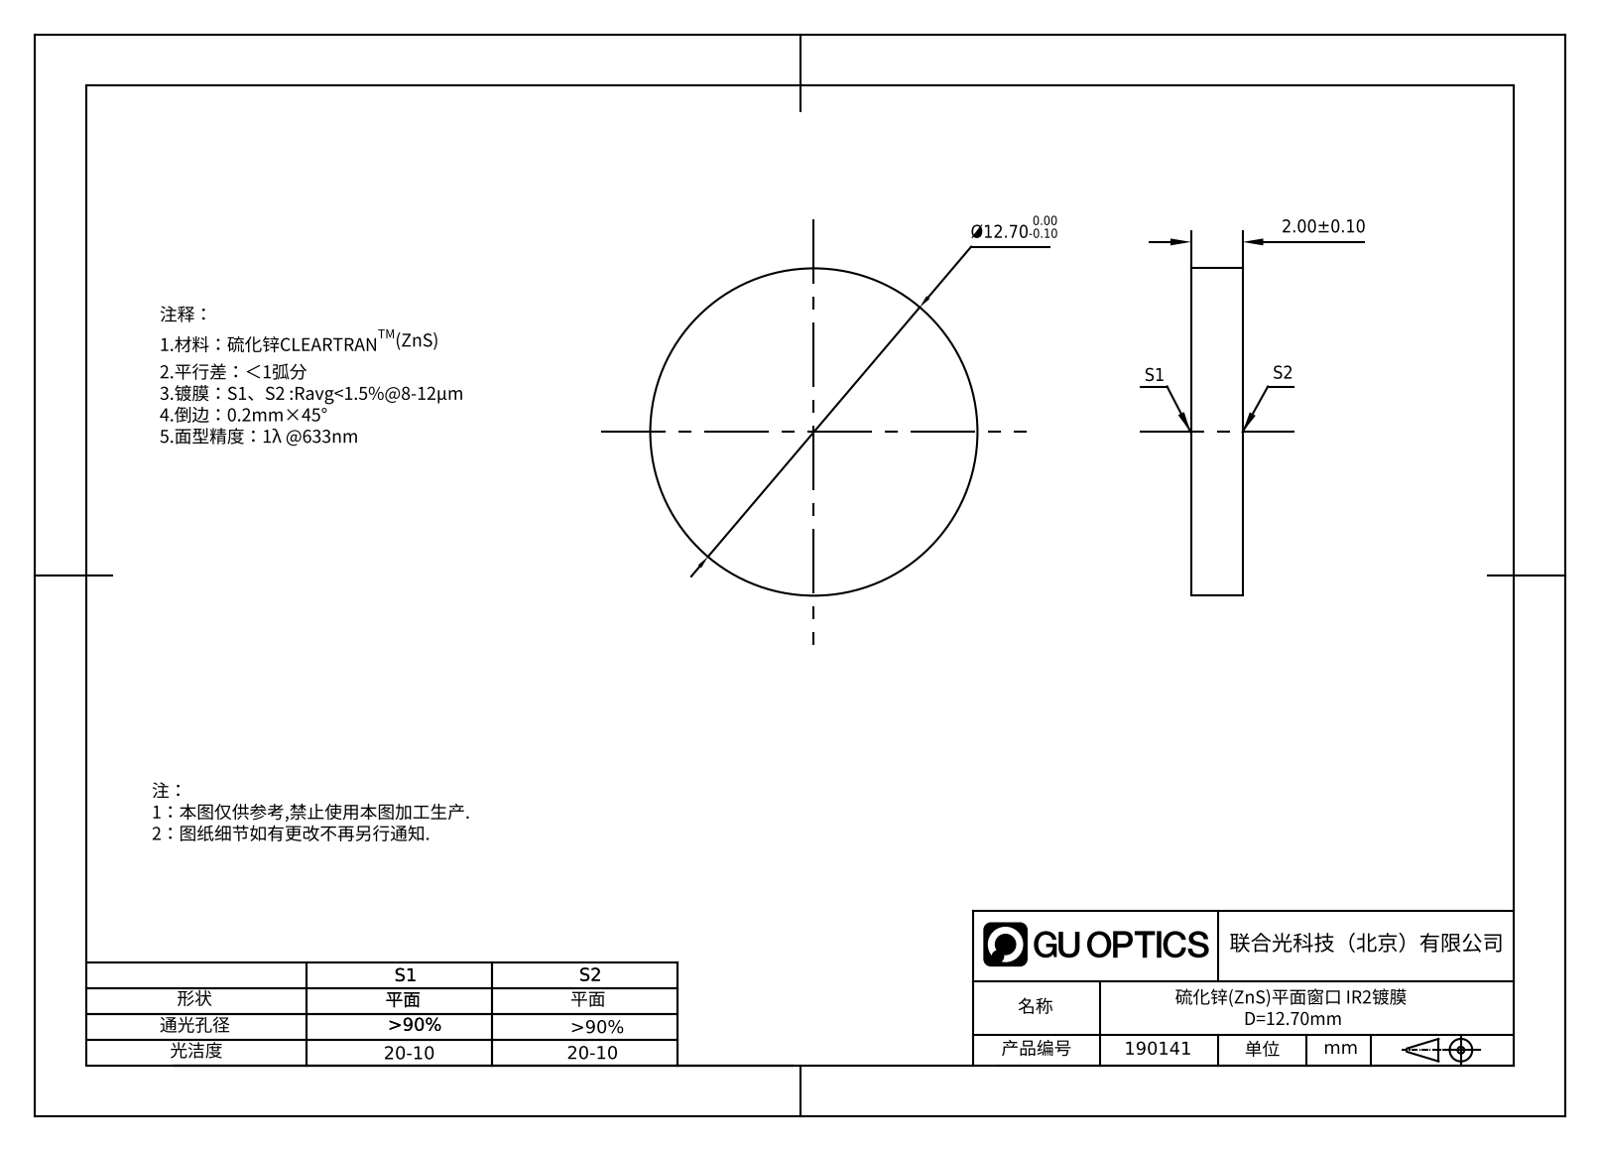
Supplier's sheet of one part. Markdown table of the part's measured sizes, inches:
| quantity | value |
| --- | --- |
| part name | 190140 |
| STEP written by | SolidWorks 2016 (AUTOMOTIVE_DESIGN) |
| units | inches |
| bodies | 1 solid, 4 faces (2 planar, 2 cylindrical, 0 other) |
| overall size | 0.5 × 0.5 × 0.079 |
| volume | 0.015 in³ |
| surface area | 0.516 in² |
| round bosses / shafts (diameter × count) | 0.5 × 1 |
| main face-to-face distances | 0.079 |
